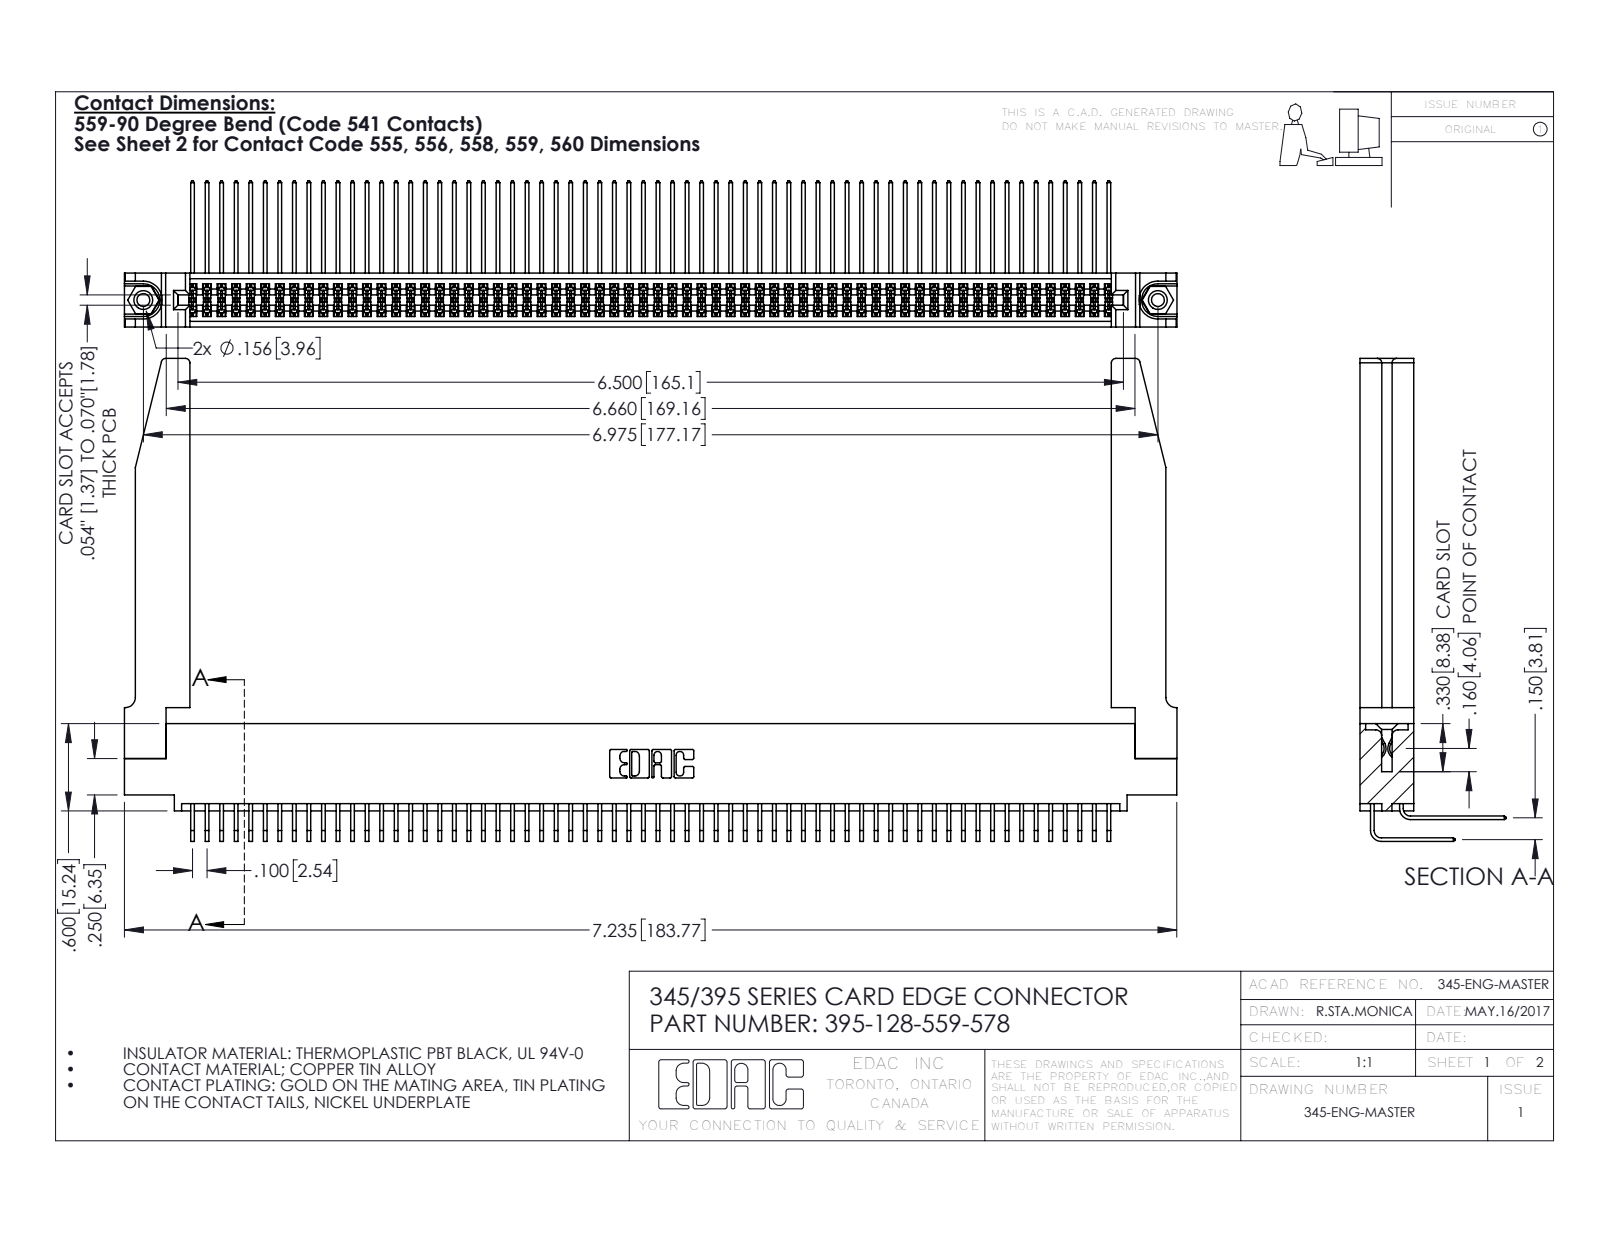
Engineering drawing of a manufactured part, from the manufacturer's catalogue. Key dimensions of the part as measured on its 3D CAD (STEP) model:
Part name (STEP PRODUCT): 345-292-001_558 559 Tail - 1; 345 Part_0.110 Offset - 0.156 Dia-TH; 345-220-078_345-220-078; 345-292-001_559 Tail - 2 (+2 more)
STEP written by: SolidWorks 2016 (CONFIG_CONTROL_DESIGN)
Units: inches
Bodies: 133 solids, 7020 faces (4706 planar, 2262 cylindrical, 52 other)
Overall size (bounding box): 7.236 × 3.319 × 1.005
Volume: 1.617 in³ · Surface area: 59.68 in²
Round holes (diameter × count): ⌀0.089 ×2, ⌀0.125 ×2, ⌀0.156 ×2, ⌀0.064 ×1
Round bosses / shafts (diameter × count): ⌀0.155 ×2
Partial cylindrical surfaces — rounded edges, fillets, slot ends (radius × count): R0.006 ×193, R0.01 ×22, R0.03 ×8, R0.007 ×6, R0.031 ×6, R0.026 ×3, R0.014 ×2, R0.019 ×2
Main face-to-face distances: 0.072, 0.298, 0.37, 0.098, 0.272, 0.025, 0.2, 0.225, 0.175, 0.15
Hole centre spacings: 0.27, 6.739, 6.975
